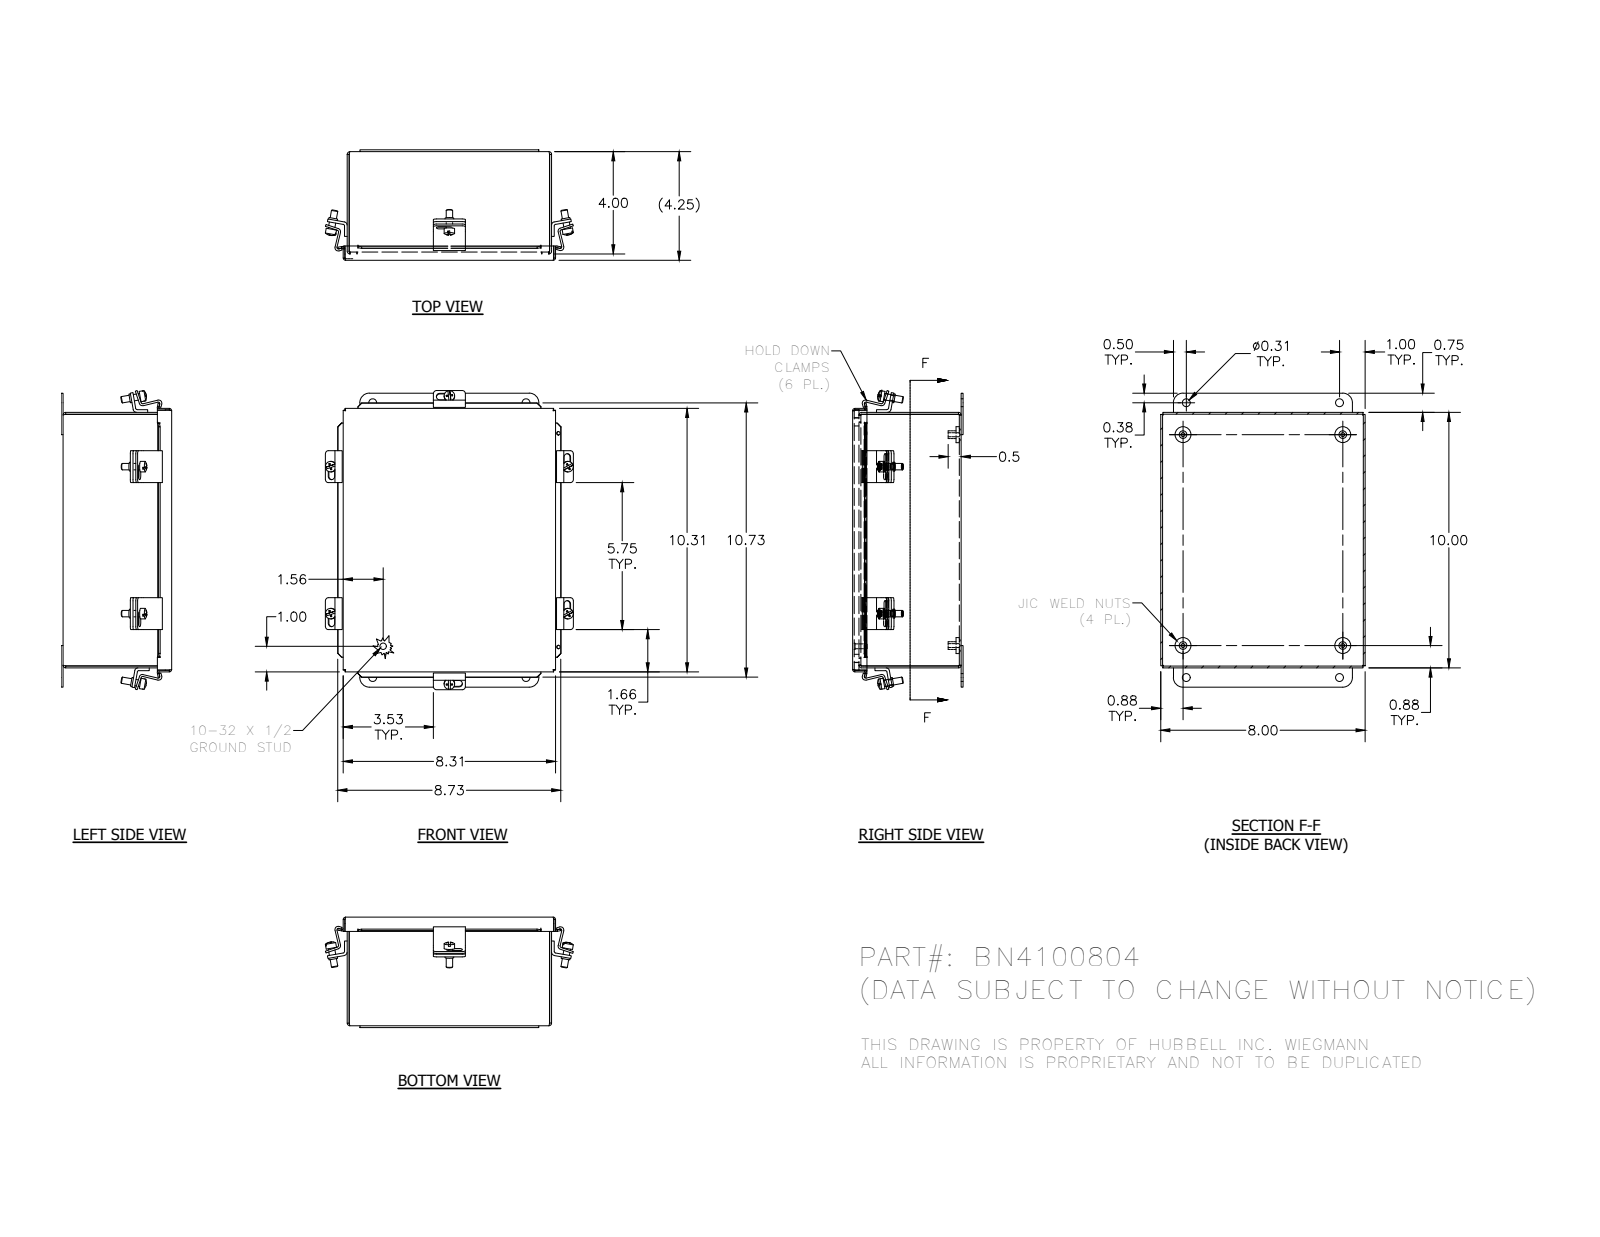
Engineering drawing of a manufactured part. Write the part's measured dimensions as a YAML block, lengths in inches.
part_name: "BN4100804; C2002_1; BN41008LID_1; 372135_1 (+6 more)"
step_written_by: "SolidWorks 2014 (AUTOMOTIVE_DESIGN)"
units: inches
bodies: {solids: 29, faces: 661, planar: 363, cylindrical: 220, other: 78}
overall_size: [11.704, 9.705, 4.324]
volume: 31.6
surface_area: 842.4
round_holes:
  - {diameter: 0.196, count: 6}
  - {diameter: 0.156, count: 4}
  - {diameter: 0.31, count: 4}
  - {diameter: 0.136, count: 2}
round_bosses_or_shafts:
  - {diameter: 0.25, count: 7}
  - {diameter: 0.41, count: 6}
  - {diameter: 0.344, count: 6}
  - {diameter: 0.625, count: 4}
  - {diameter: 0.3, count: 4}
  - {diameter: 0.19, count: 1}
partial_cylinders:
  - {radius: 0.125, count: 24}
  - {radius: 0.031, count: 16}
  - {radius: 0.063, count: 12}
  - {radius: 0.126, count: 12}
  - {radius: 0.133, count: 12}
  - {radius: 0.093, count: 8}
  - {radius: 0.105, count: 8}
  - {radius: 0.375, count: 4}
face_to_face_distances: [0.074, 4.187, 0.062, 4.25, 4.113, 4.176, 7.926, 9.926, 3.926, 8]
hole_center_spacings: [1.256, 9.501, 5.75, 6, 6.25, 6.251, 6.252, 8.25]
